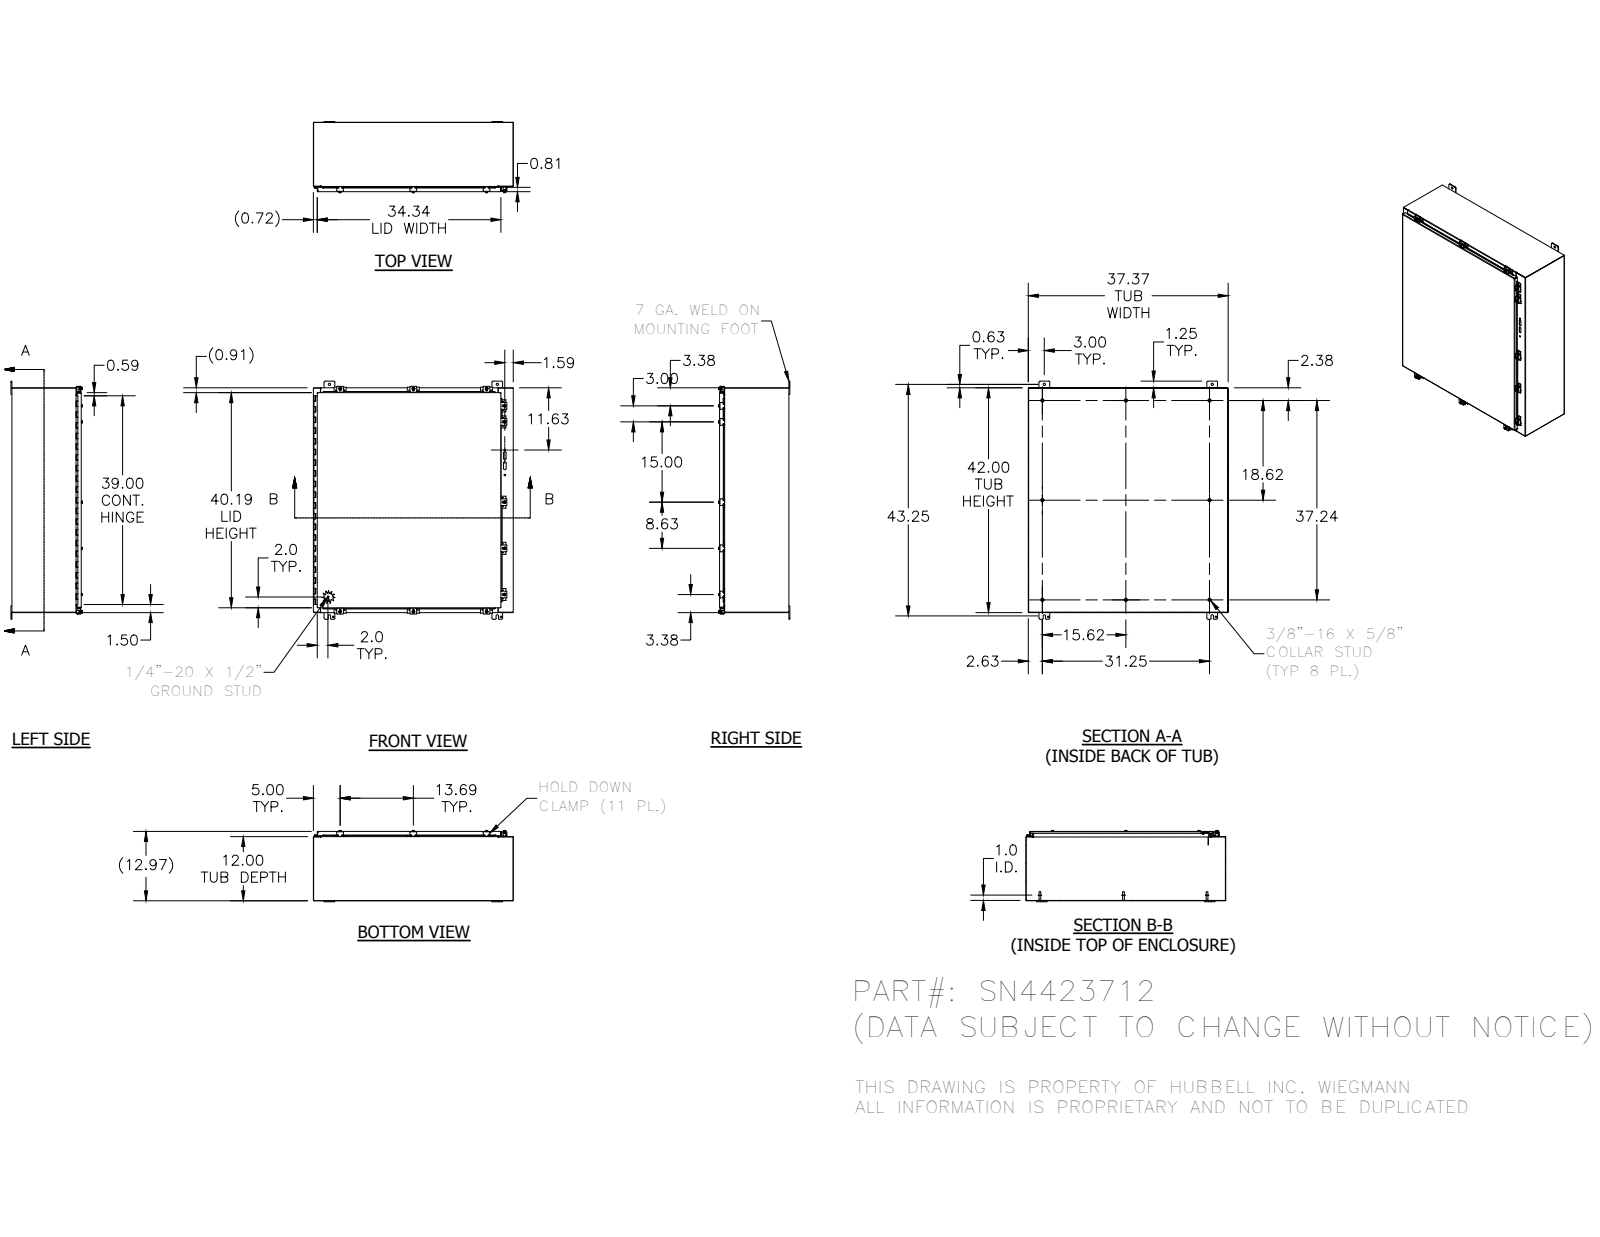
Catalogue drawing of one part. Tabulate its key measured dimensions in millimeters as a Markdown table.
| quantity | value |
| --- | --- |
| part name | SN4423712BLR; 3889; 34840; SN44237LID (+8 more) |
| STEP written by | Autodesk Inventor 2016 (AUTOMOTIVE_DESIGN) |
| units | millimeters |
| bodies | 80 solids, 2200 faces (1203 planar, 681 cylindrical, 316 other) |
| overall size | 1130.3 × 949.33 × 338.45 |
| volume | 6 716 000 mm³ |
| surface area | 7 156 000 mm² |
| round holes (diameter × count) | 2.79 × 22, 7.14 × 13, 5.36 × 11, 7.62 × 11, 7.95 × 4, 11.13 × 4, 3.96 × 2, 3.17 × 1 |
| round bosses / shafts (diameter × count) | 6.35 × 15, 13.21 × 11, 12.7 × 11, 8.89 × 11, 8.38 × 9, 15.88 × 8, 4.83 × 2, 2.92 × 2 |
| partial cylindrical surfaces (radius × count) | 0.76 × 127, 6.35 × 39, 3.17 × 34, 1.59 × 23, 3.57 × 22, 0.79 × 21, 2.67 × 21, 2.54 × 16 |
| main face-to-face distances | 1.88, 327.59, 325.71, 329.47, 947.45, 1064.92, 302.92, 24.67, 949.33, 945.57 |
| hole center spacings | 1052.12, 22.26, 347.66, 368.39, 1099.97, 1101.58, 1114.53, 327.14 |
